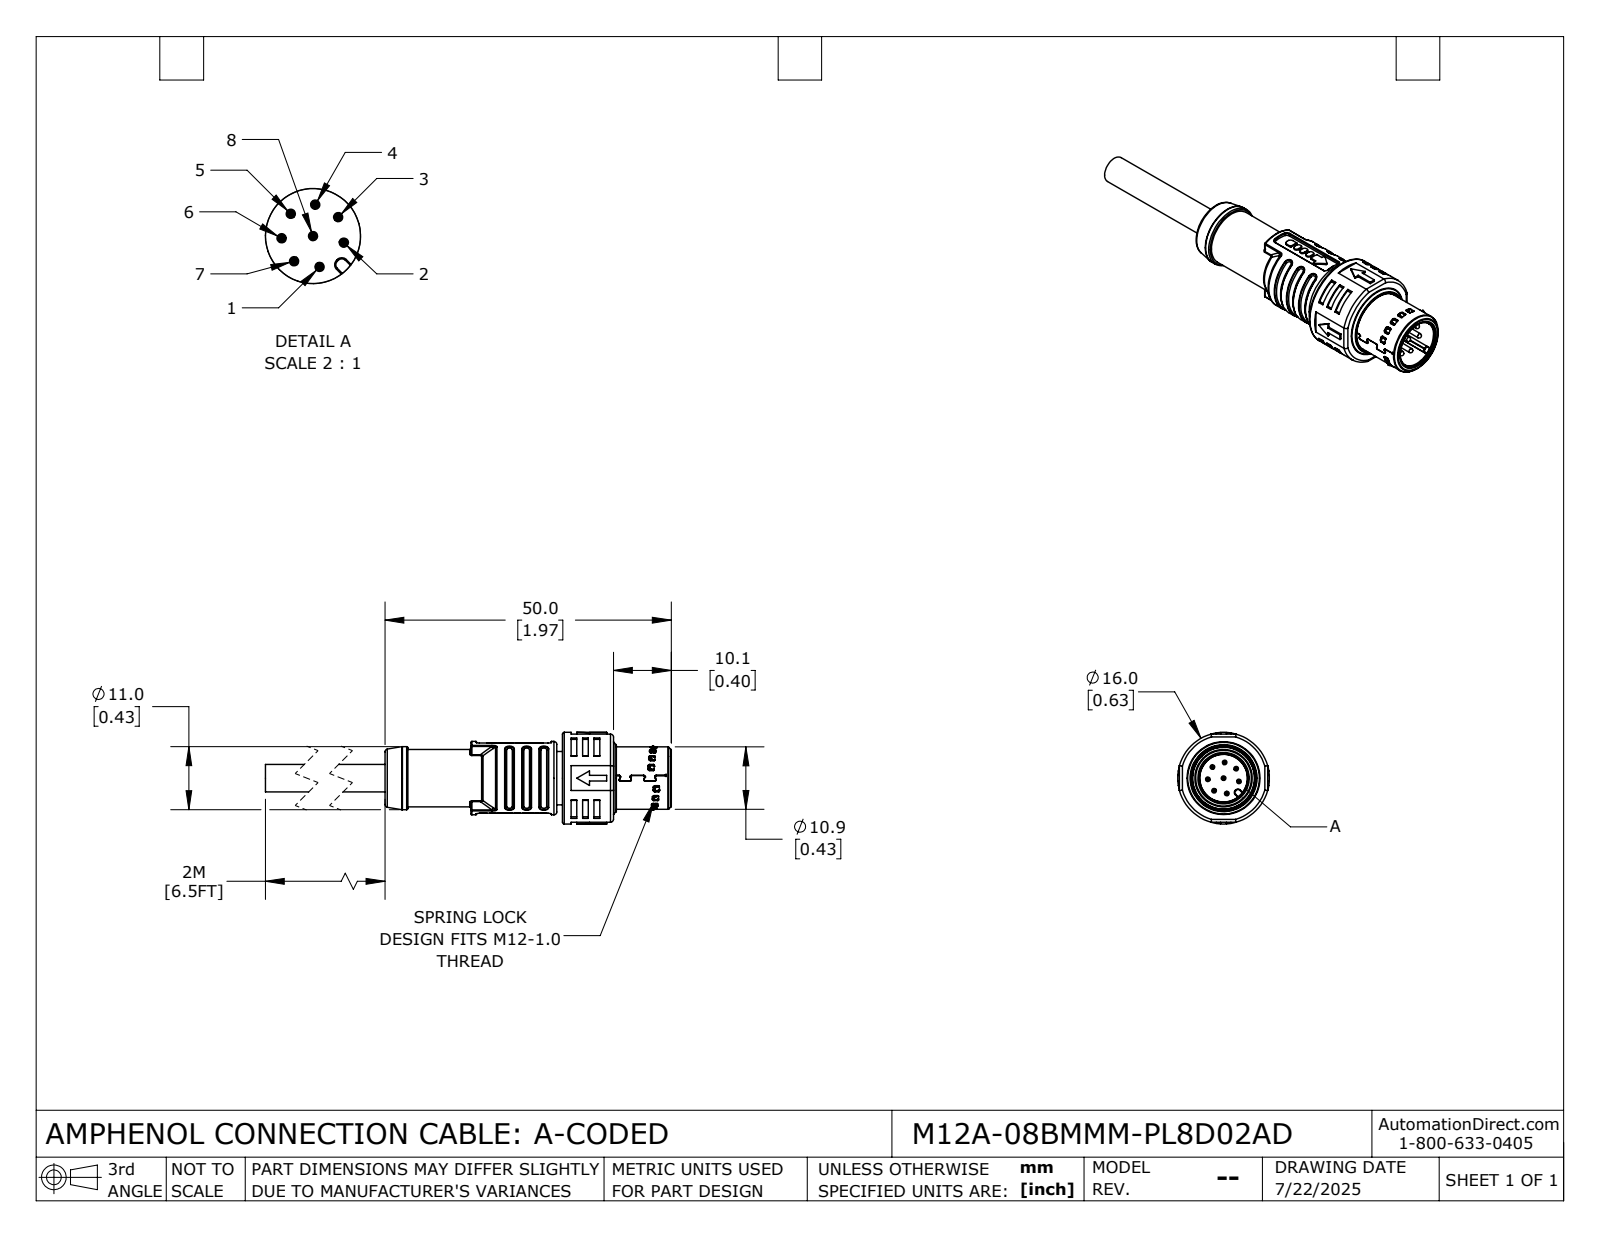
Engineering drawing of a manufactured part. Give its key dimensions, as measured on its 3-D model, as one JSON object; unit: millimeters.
{"part_name": "M12A-08BMMM-PL8D02AD", "step_written_by": "SolidWorks 2024 (CONFIG_CONTROL_DESIGN)", "units": "millimeters", "bodies": {"solids": 1, "faces": 2027, "planar": 880, "cylindrical": 644, "other": 503}, "overall_size": [75, 16, 16], "volume_mm3": 5223, "surface_area_mm2": 5723, "round_holes": [[8.3, 1], [9, 1], [10.15, 1], [10.5, 1], [10.9, 1], [11.5, 1], [11.8, 1], [14.2, 1]], "round_bosses_or_shafts": [[0.8, 8], [16, 1], [14.1, 1], [12.8, 1], [12.4, 1], [11, 1], [10.45, 1], [10.4, 1]], "partial_cylinders_radius": [[0.2, 114], [0.25, 66], [0.3, 64], [0.15, 44], [0.5, 38], [0.13, 12], [0.7, 11], [0.1, 10]], "face_to_face_distances": [1, 10.1, 8.6, 8.9, 2.5, 1.5, 1.2, 32.5, 15.4, 41.1]}
